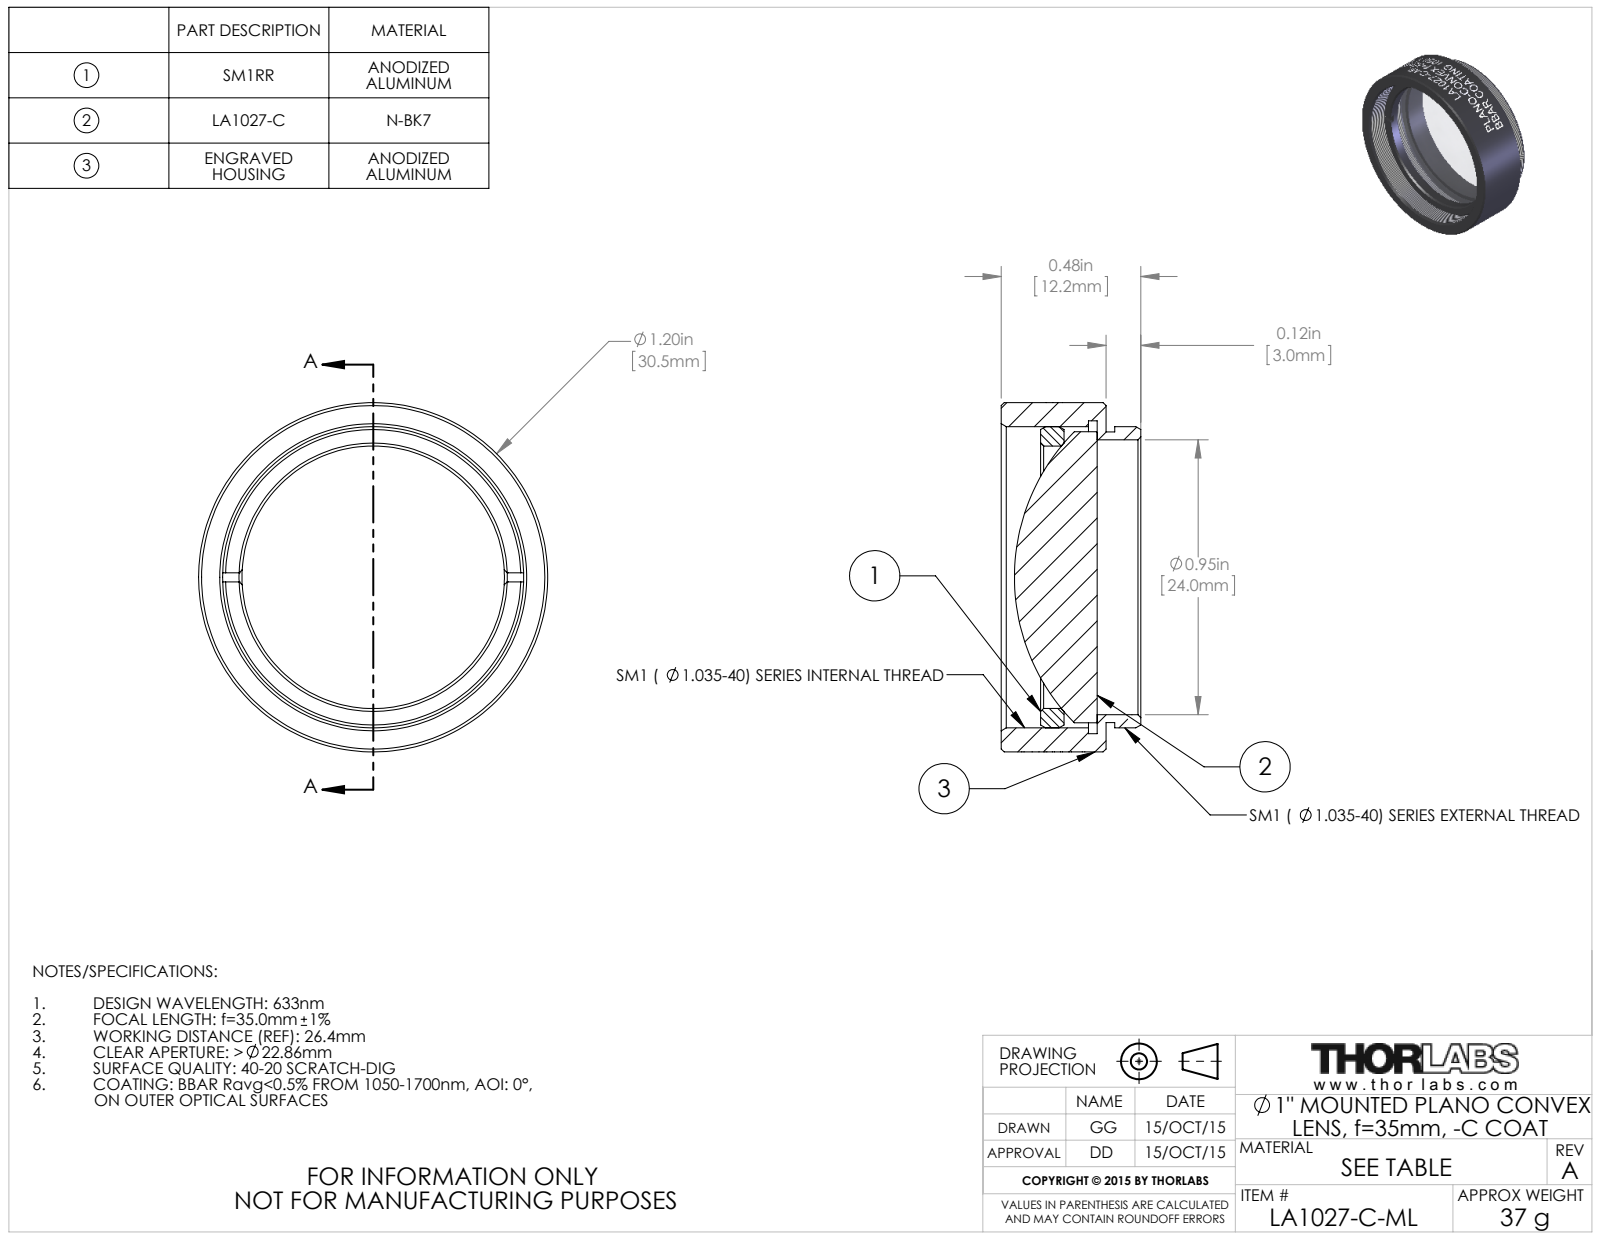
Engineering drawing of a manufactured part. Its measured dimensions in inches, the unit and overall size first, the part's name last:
Units: inches
Overall size (bounding box): 1.2 × 1.2 × 0.48
Round holes (diameter × count): ⌀0.902 ×1, ⌀0.945 ×1, ⌀1.075 ×1
Round bosses / shafts (diameter × count): ⌀1.2 ×1, ⌀1.035 ×1, ⌀1 ×1, ⌀0.999 ×1
Main face-to-face distances: 0.03, 0.36, 0.33, 0.144, 0.115, 0.215, 0.224, 0.194, 0.08, 0.135
Volume: 0.283 in³ · Surface area: 7.023 in²
Bodies: 3 solids, 153 faces (20 planar, 105 cylindrical, 28 other)
Part name (STEP PRODUCT): TTN039480-E0W
STEP written by: SolidWorks 2014 (CONFIG_CONTROL_DESIGN)
